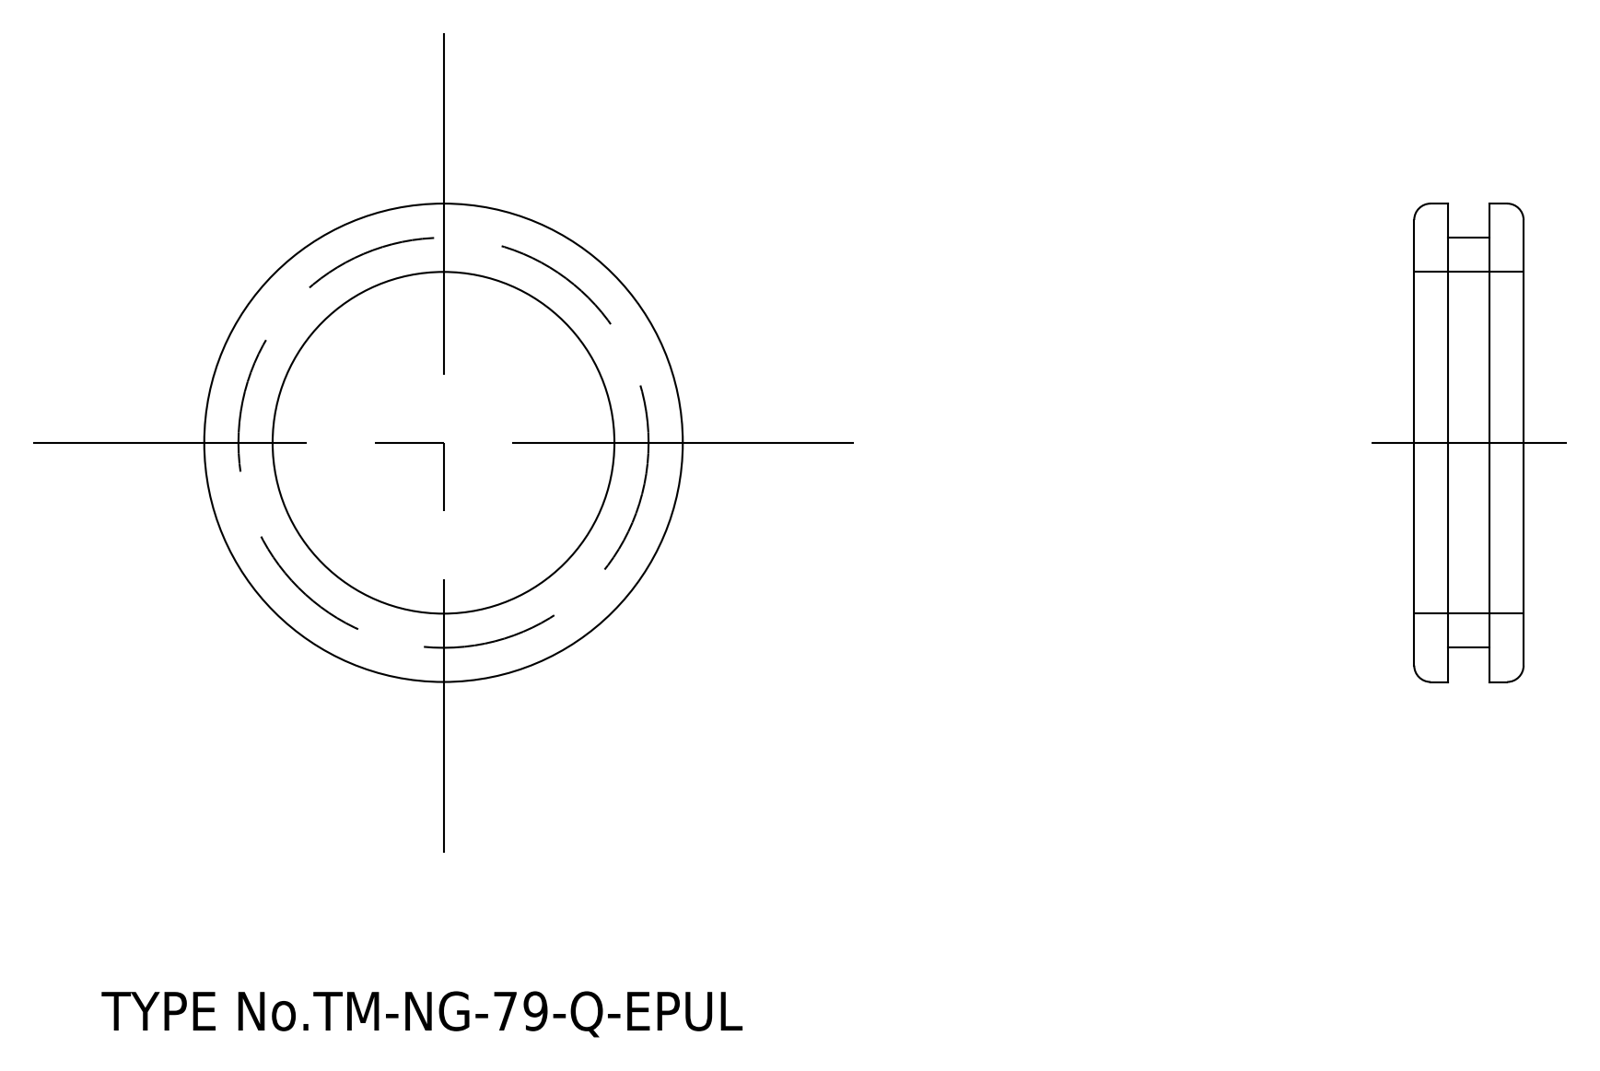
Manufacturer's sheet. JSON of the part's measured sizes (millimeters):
{"step_written_by": "spGate 15.6.1 (AUTOMOTIVE_DESIGN)", "units": "millimeters", "bodies": {"solids": 1, "faces": 16, "planar": 4, "cylindrical": 8, "other": 4}, "overall_size": [35, 35, 8], "volume_mm3": 2939, "surface_area_mm2": 2799, "round_holes": [[25, 1]], "round_bosses_or_shafts": [[35, 1], [30, 1]], "face_to_face_distances": [2.5, 5.5, 8, 3]}
